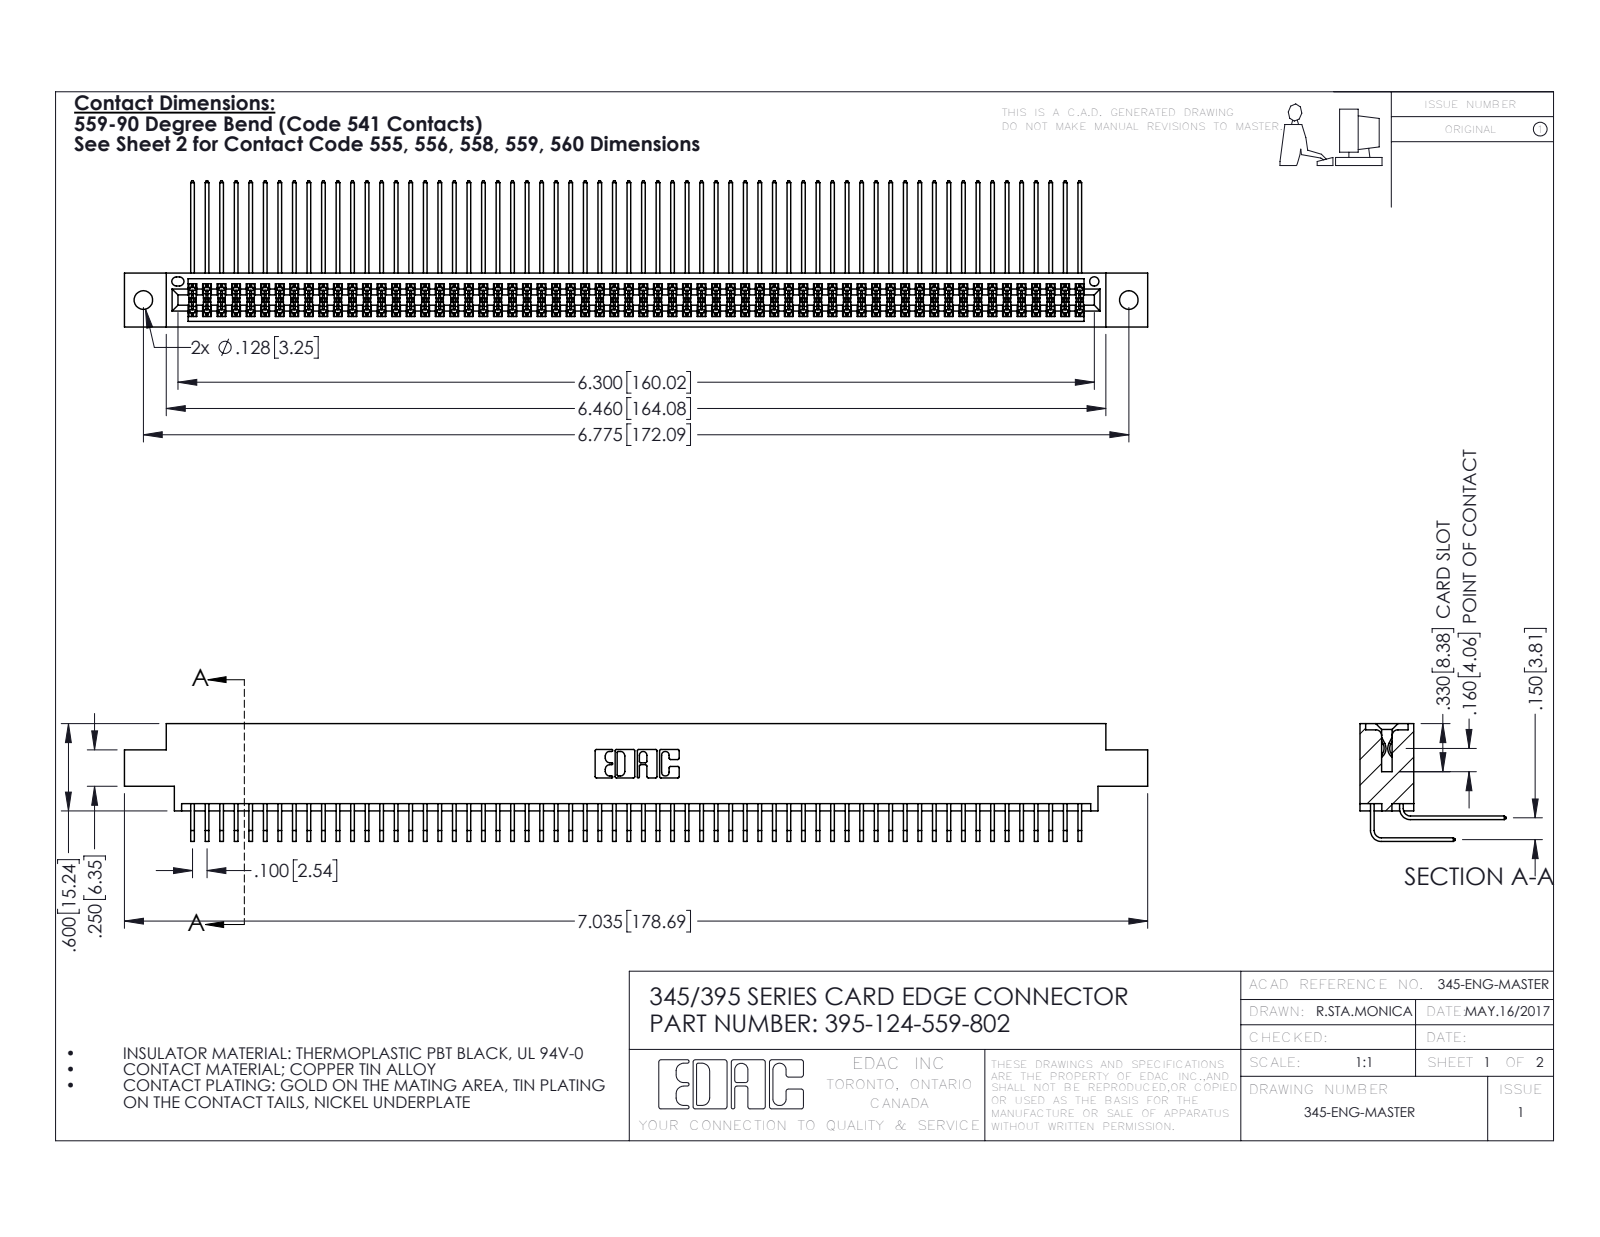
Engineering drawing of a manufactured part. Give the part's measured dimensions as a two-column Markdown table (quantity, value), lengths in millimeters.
| quantity | value |
| --- | --- |
| part name | 345-292-001_558 559 Tail - 1; 395-124-559-802; 345-292-001_559 Tail - 2; 345 Part_0.170 Offset - 0.128 Dia |
| STEP written by | SolidWorks 2016 (CONFIG_CONTROL_DESIGN) |
| units | millimeters |
| bodies | 125 solids, 6578 faces (4424 planar, 2154 cylindrical, 0 other) |
| overall size | 178.7 × 25.5 × 20.5 |
| volume | 18 110 mm³ |
| surface area | 30 390 mm² |
| round holes (diameter × count) | 3.3 × 2, 1.6 × 1 |
| partial cylindrical surfaces (radius × count) | 0.2 × 186, 0.3 × 22, 0.2 × 6, 0.8 × 6, 0.7 × 3, 0.4 × 2, 0.5 × 2, 0.6 × 2 |
| main face-to-face distances | 1.8, 7.6, 9.4, 5.1, 2.5, 6.9, 0.6, 5.7, 4.4, 3.8 |
| hole center spacings | 6.9, 166.1, 172.1 |
